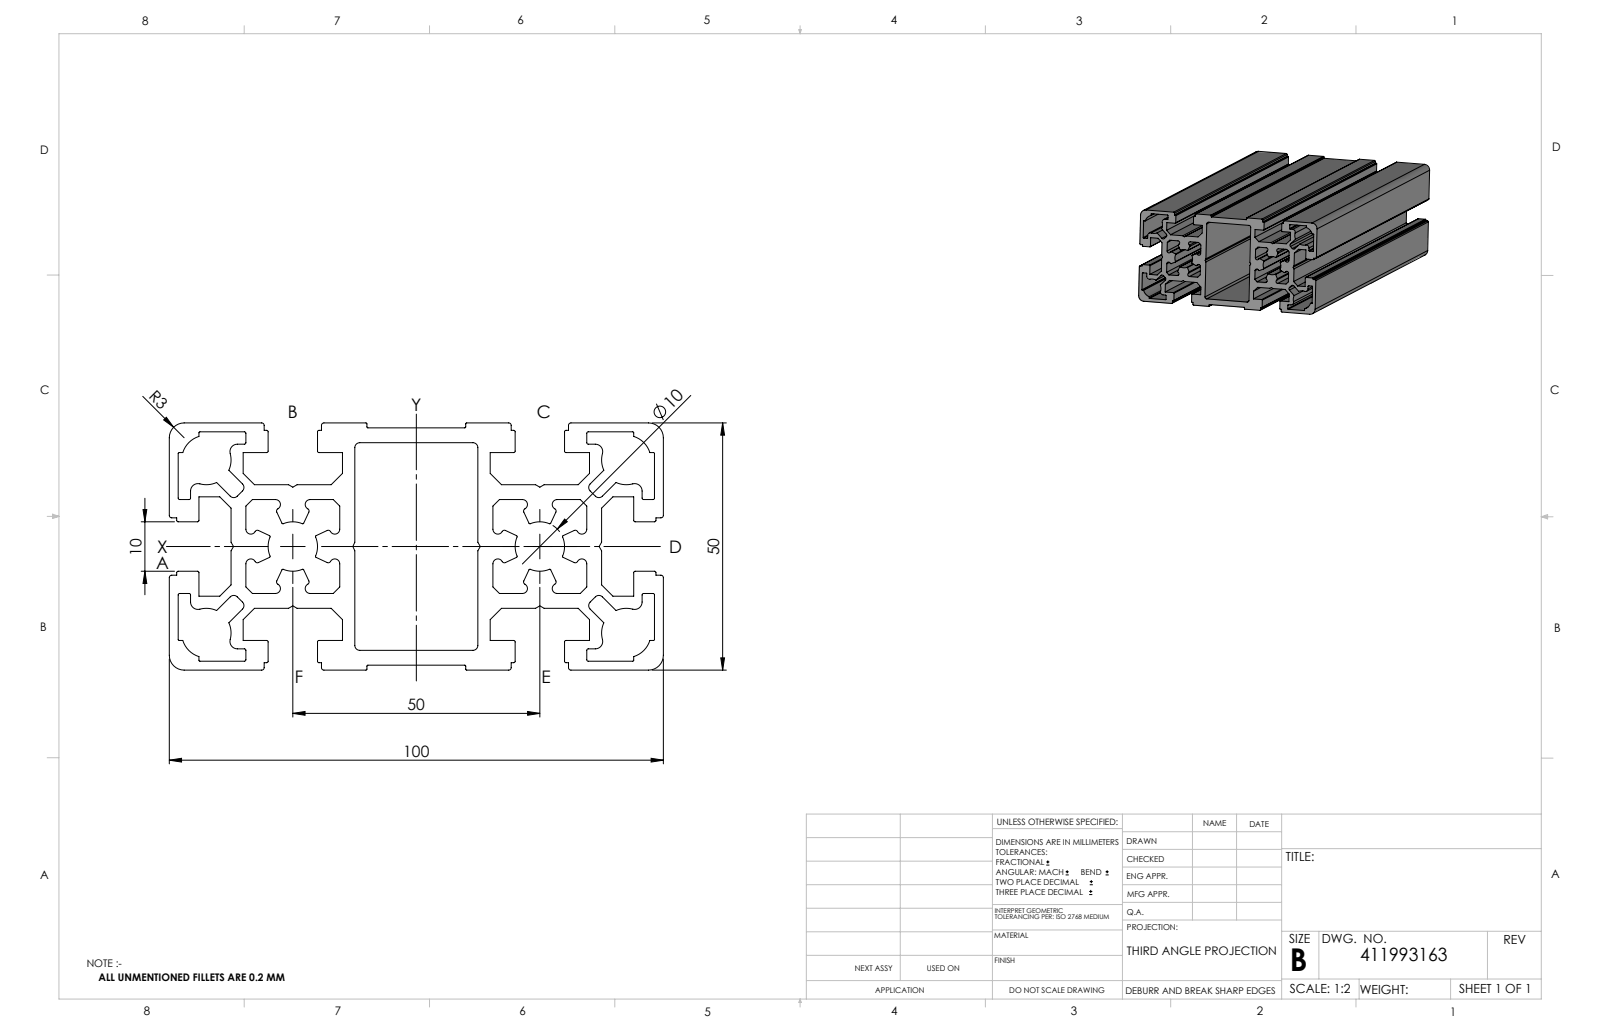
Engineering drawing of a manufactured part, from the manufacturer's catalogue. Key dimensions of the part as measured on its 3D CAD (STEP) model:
Part name (STEP PRODUCT): 411993163_c_1
STEP written by: SolidWorks 2014 (CONFIG_CONTROL_DESIGN)
Units: millimetres
Bodies: 1 solid, 390 faces (210 planar, 180 cylindrical, 0 other)
Overall size (bounding box): 200 × 100 × 50
Volume: 350 233 mm³ · Surface area: 230 706 mm²
Partial cylindrical surfaces — rounded edges, fillets, slot ends (radius × count): R0.3 ×40, R0.2 ×32, R0.5 ×28, R1 ×28, R1.5 ×8, R5 ×6, R3 ×4
Main face-to-face distances: 3, 33.5, 11.5, 50, 12.5, 1.8, 15.5, 14.5, 34.5, 22
